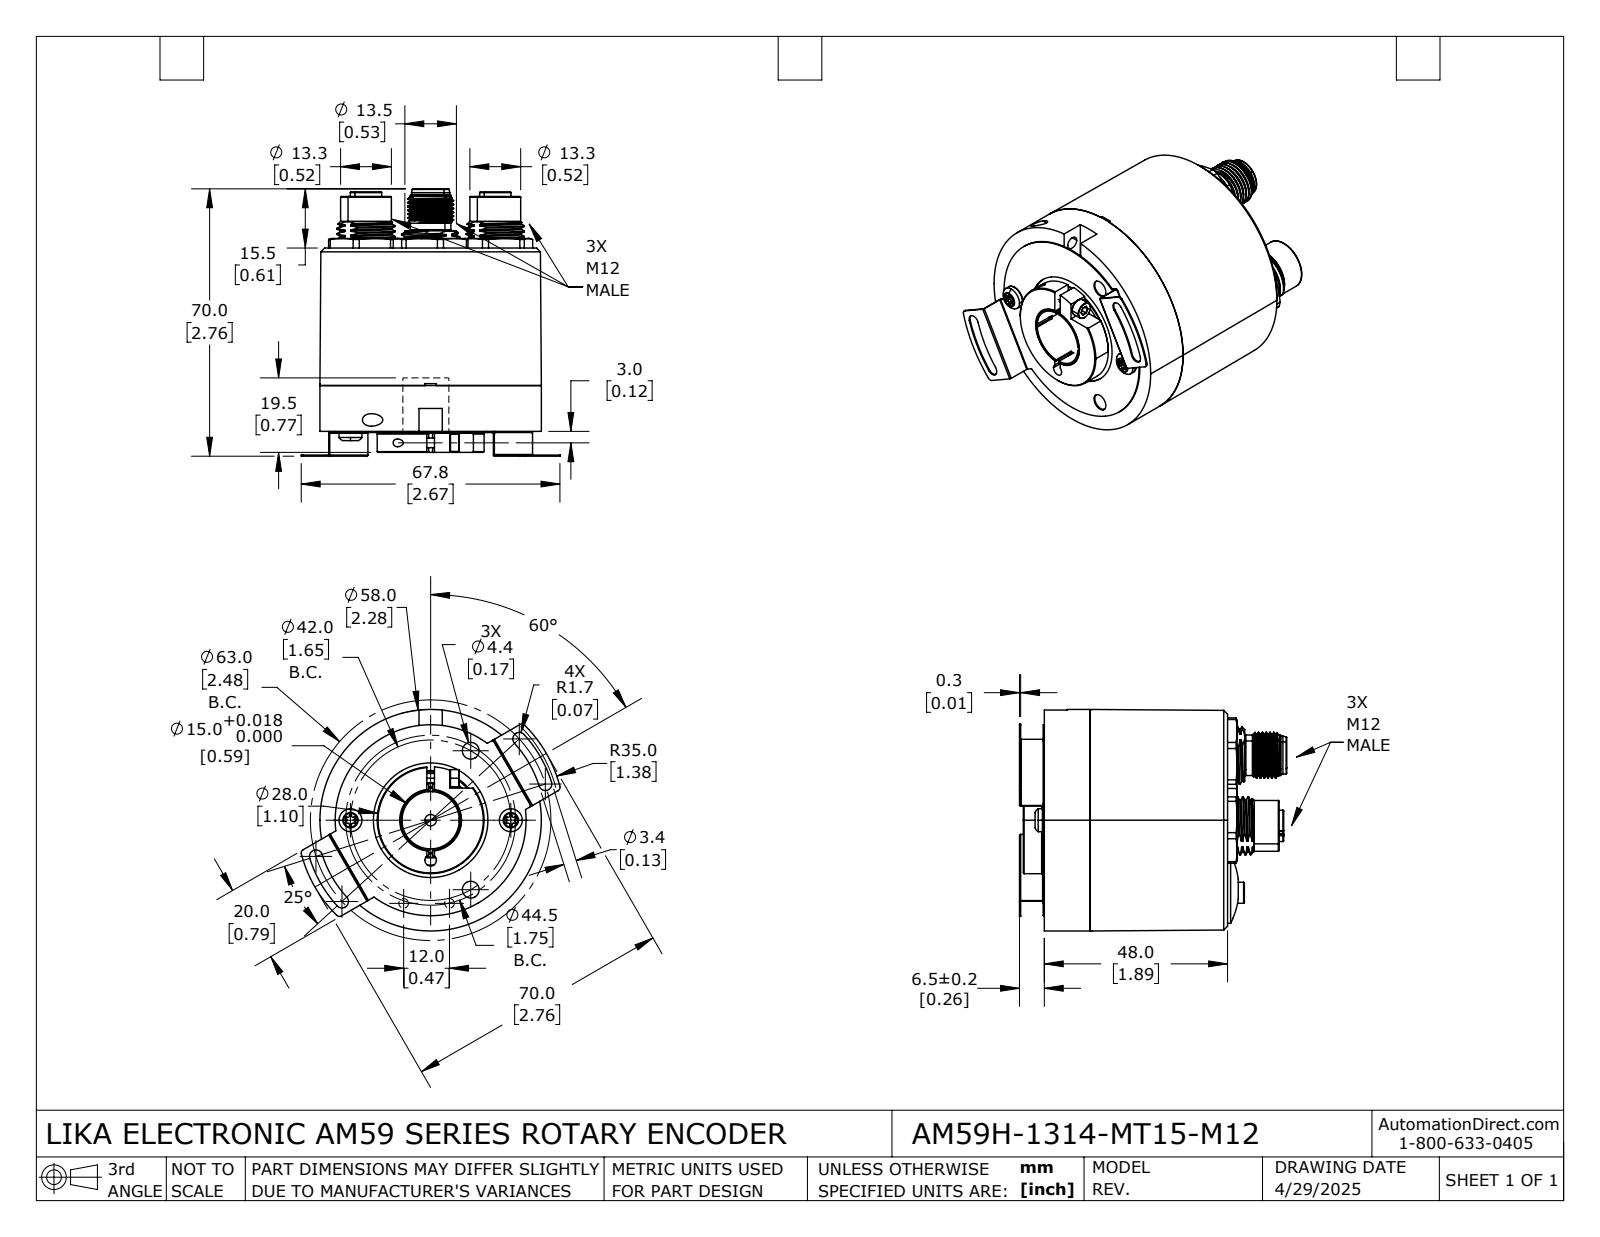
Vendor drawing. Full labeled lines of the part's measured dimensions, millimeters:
Part name (STEP PRODUCT): AM59H-1314-MT15-M12
STEP written by: SolidWorks 2024 (AUTOMOTIVE_DESIGN)
Units: millimetres
Bodies: 55 solids, 1648 faces (438 planar, 595 cylindrical, 615 other)
Overall size (bounding box): 70 × 67.8 × 58
Volume: 64 970 mm³ · Surface area: 54 660 mm²
Round holes (diameter × count): ⌀2 ×11, ⌀1.2 ×10, ⌀2.5 ×8, ⌀2.1 ×6, ⌀3.5 ×5, ⌀1.6 ×4, ⌀12.5 ×3, ⌀3.2 ×2, ⌀4.4 ×2, ⌀9.7 ×2, ⌀10.9 ×2, ⌀1 ×1
Round bosses / shafts (diameter × count): ⌀1.6 ×12, ⌀1 ×12, ⌀3 ×8, ⌀13.3 ×3, ⌀6 ×3, ⌀58 ×1, ⌀55.5 ×1, ⌀55 ×1
Partial cylindrical surfaces — rounded edges, fillets, slot ends (radius × count): R1 ×29, R0.2 ×26, R0.3 ×12, R0.4 ×12, R0.1 ×6, R0.2 ×4, R0.3 ×4, R1.7 ×4
Main face-to-face distances: 2.5, 45.5, 48, 48.3, 45.8, 15.3, 33, 0.5, 20, 17.5
Hole centre spacings: 21, 5.3, 7.5, 15, 20.1, 21.2, 24.5, 32.3
